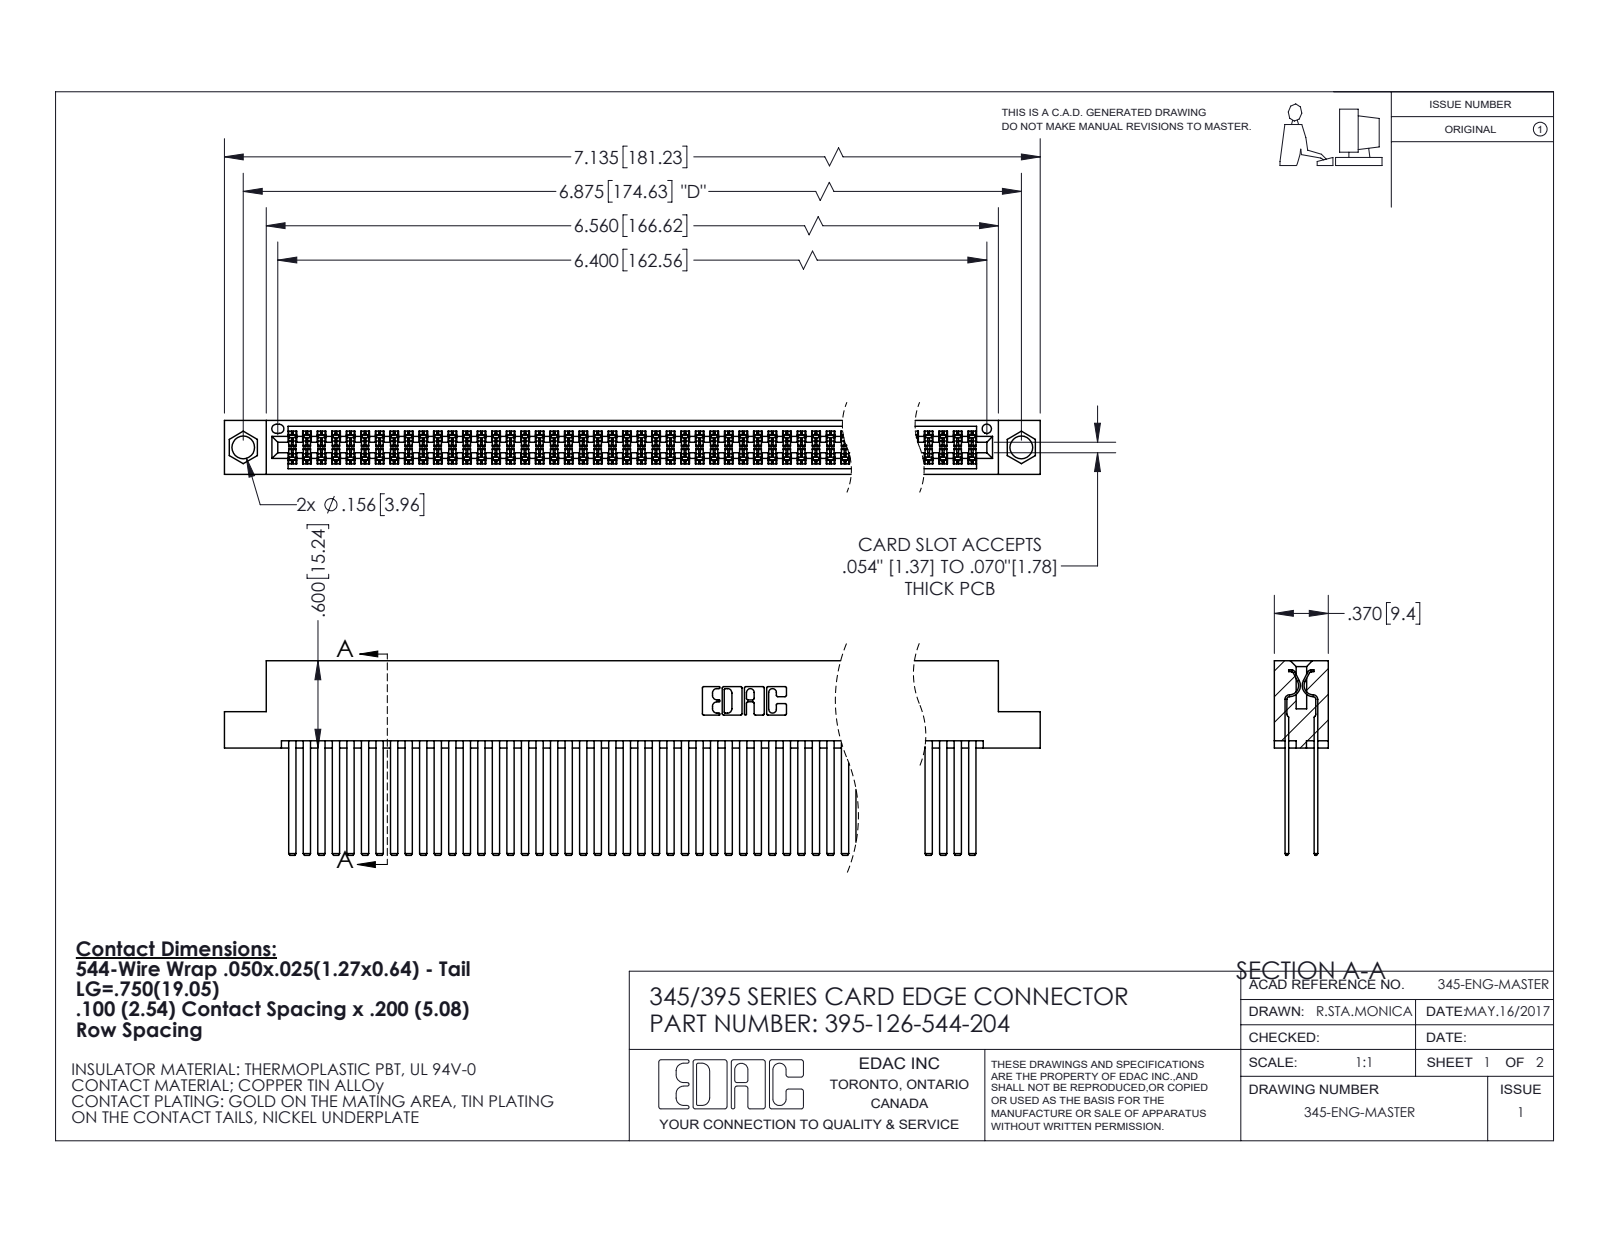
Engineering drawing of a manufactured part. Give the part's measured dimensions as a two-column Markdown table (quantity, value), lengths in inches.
| quantity | value |
| --- | --- |
| part name | 345-292-001_345-293-144; 345 Part_Flush Mounting Lugs - 0.156 Dia-TI; 395-126-544-204 |
| STEP written by | SolidWorks 2020 (CONFIG_CONTROL_DESIGN) |
| units | inches |
| bodies | 127 solids, 5684 faces (3748 planar, 1936 cylindrical, 0 other) |
| overall size | 7.135 × 1.337 × 0.37 |
| volume | 1.188 in³ |
| surface area | 53.01 in² |
| round holes (diameter × count) | 0.156 × 2, 0.064 × 1 |
| partial cylindrical surfaces (radius × count) | 0.006 × 189, 0.01 × 22, 0.007 × 6, 0.031 × 6, 0.026 × 3, 0.014 × 2, 0.019 × 2, 0.022 × 2 |
| main face-to-face distances | 0.2, 0.025, 0.298, 0.072, 0.098, 0.272, 0.225, 0.175, 0.37, 0.05 |
| hole center spacings | 0.27, 6.639, 6.875 |
